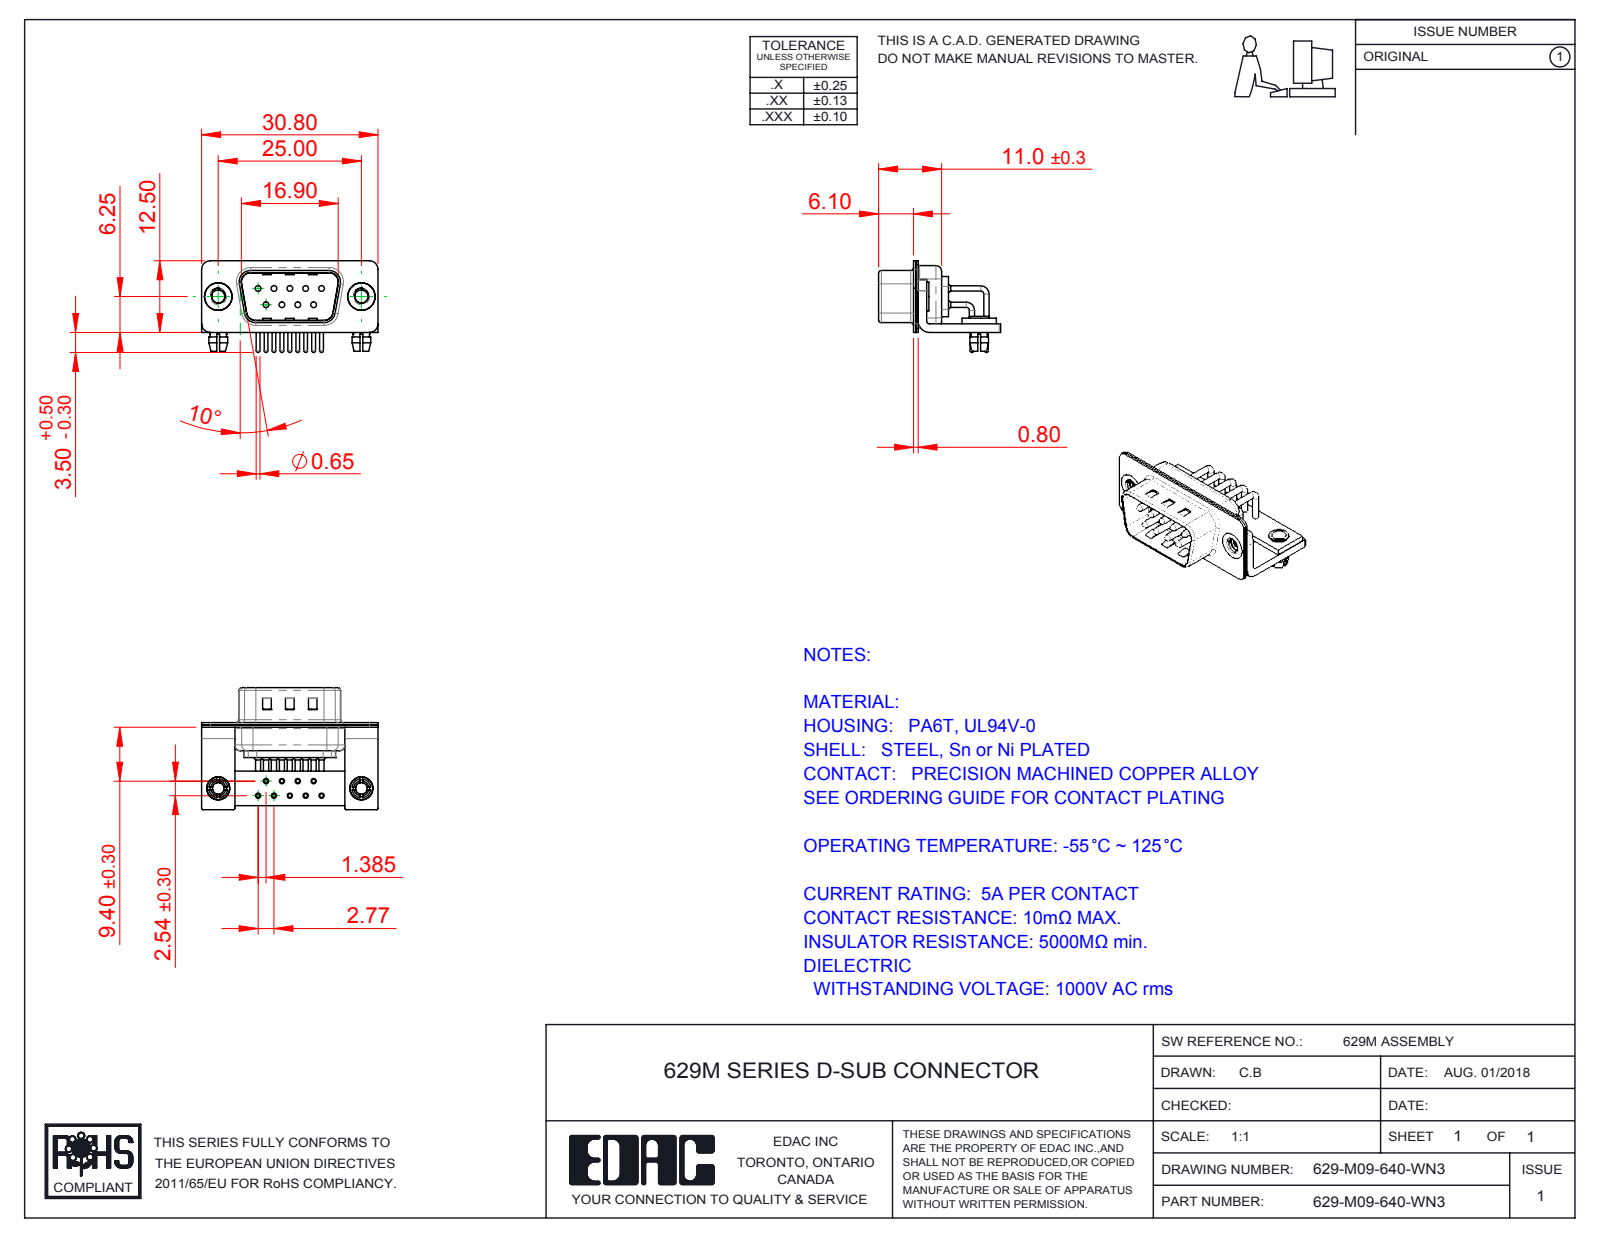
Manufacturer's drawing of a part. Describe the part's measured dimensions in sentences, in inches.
The part is named "629-M09-640-WN3; 629M Board Lock; 629M Stabilizer Board_09 Contacts; 629M Stabilizer Bracket (+6 more)". Its 3-D file was written by "SolidWorks 2016 (CONFIG_CONTROL_DESIGN)". It is 19 solids with 1454 faces: 757 planar, 525 cylindrical and 172 other. Overall it measures 1.213 by 0.839 by 0.63 inches. Its volume is 0.113 cubic inches and its surface area 8.035 square inches. Round holes: 11 of diameter 0.079, 9 of diameter 0.035, 9 of diameter 0.039, 9 of diameter 0.067, 2 of diameter 0.089, 2 of diameter 0.098, 2 of diameter 0.126, 2 of diameter 0.157, 2 of diameter 0.189. Round bosses or shafts: 9 of diameter 0.059, 9 of diameter 0.035, 9 of diameter 0.026, 2 of diameter 0.197, 2 of diameter 0.193, 2 of diameter 0.157, 2 of diameter 0.134, 2 of diameter 0.13. Partial cylindrical surfaces (rounded edges, fillets, slot ends): 16 of radius 0.01, 16 of radius 0.059, 13 of radius 0.079, 9 of radius 0.02, 9 of radius 0.04, 8 of radius 0.063, 4 of radius 0.024, 4 of radius 0.026. The main face-to-face distances are 0.016, 0.059, 0.031, 0.033, 0.049, 0.075, 0.039, 0.098, 0.409, 0.376. The hole center spacings are 0.109, 0.218, 0.124, 0.192, 0.327, 0.114, 0.114, 0.198.
